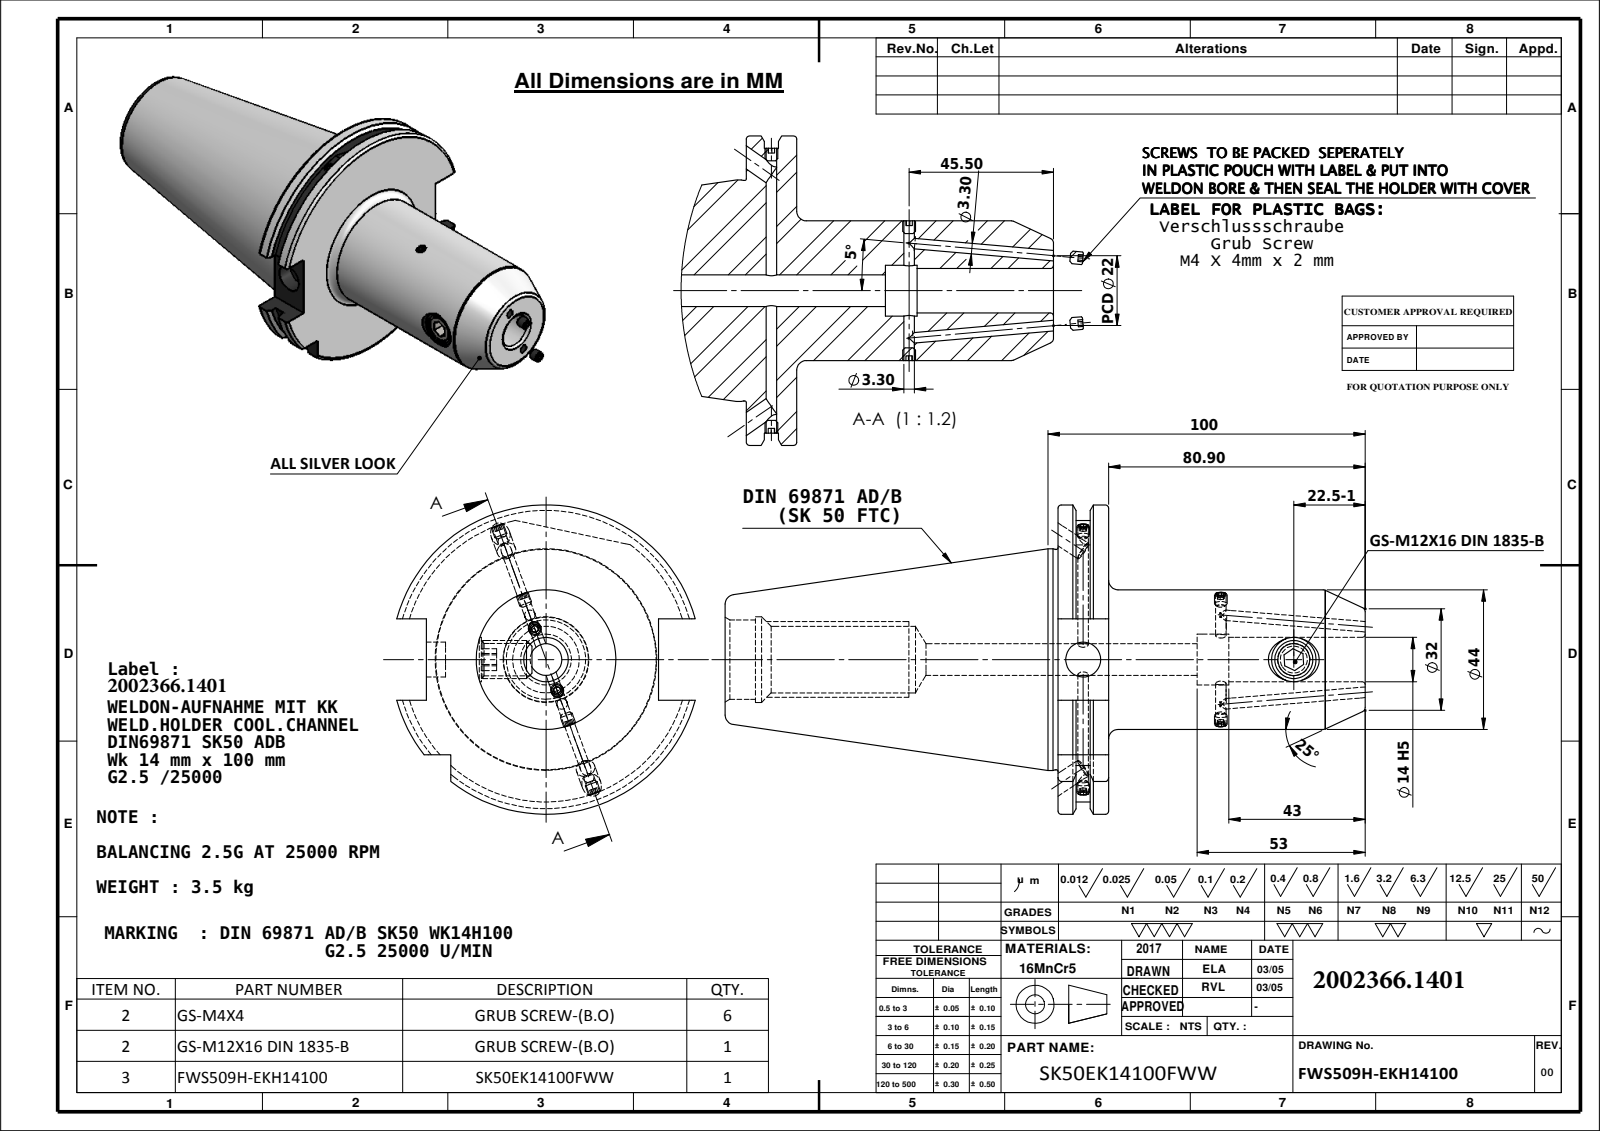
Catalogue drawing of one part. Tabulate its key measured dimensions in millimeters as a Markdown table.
| quantity | value |
| --- | --- |
| part name | 91506-WK214100; SK50EK140100FWW; M12X16_ISO 4026 - M12 x 12-N; Copy of M4X4_DIN 913 - M4 x 4-N |
| STEP written by | SolidWorks 2009 (CONFIG_CONTROL_DESIGN) |
| units | millimeters |
| bodies | 8 solids, 244 faces (93 planar, 77 cylindrical, 74 other) |
| overall size | 211.17 × 97.5 × 94.05 |
| volume | 440 580 mm³ |
| surface area | 59 641 mm² |
| round holes (diameter × count) | 3.3 × 4, 6 × 2, 14 × 2, 10 × 1, 10.2 × 1, 11 × 1, 16 × 1, 21 × 1, 25 × 1, 27 × 1 |
| round bosses / shafts (diameter × count) | 4 × 6, 69.85 × 1, 69.45 × 1, 44 × 1, 12 × 1 |
| partial cylindrical surfaces (radius × count) | 44.9 × 1, 48.75 × 1 |
| main face-to-face distances | 15.9, 10.15, 5.75, 5.66, 4.49, 10.24, 96.8, 91.14, 86.65, 80.9 |
| hole center spacings | 43.4, 66.4 |
